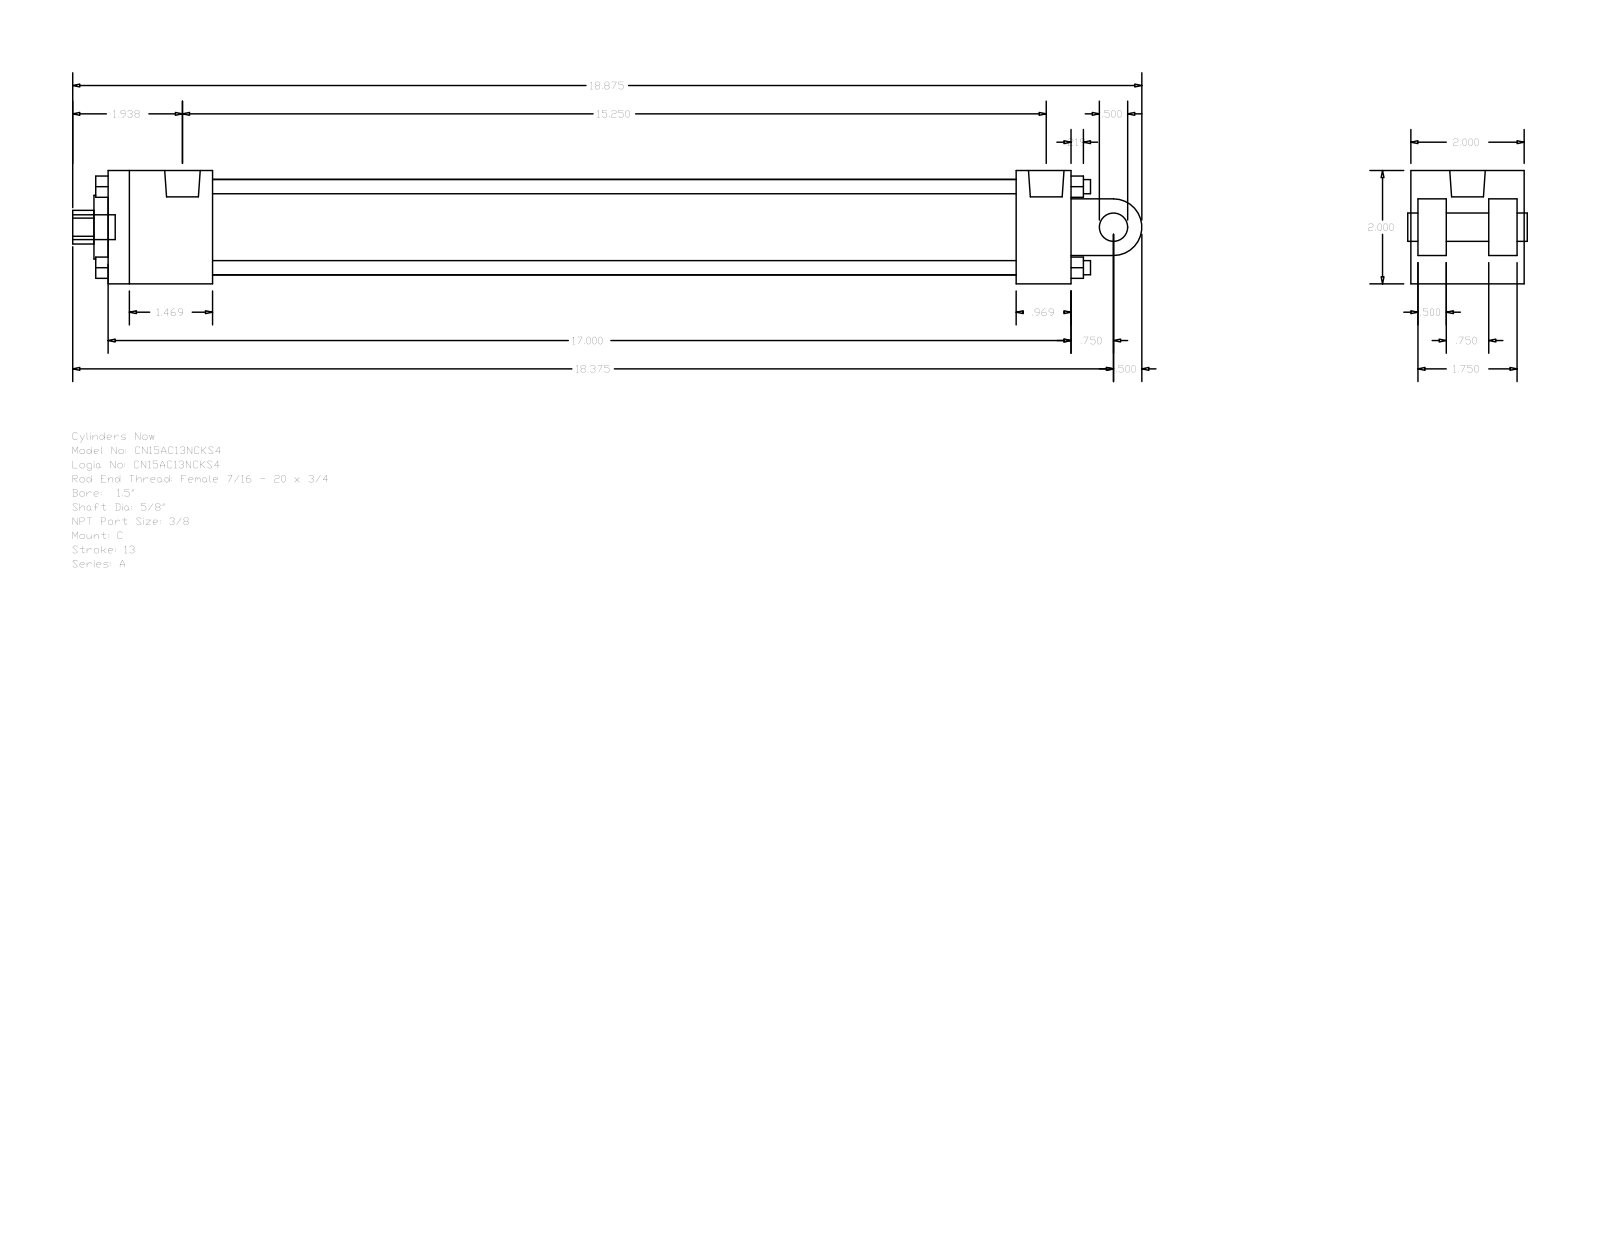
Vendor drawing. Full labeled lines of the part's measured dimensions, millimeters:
Part name (STEP PRODUCT): A_C__0150_0.625
STEP written by: GSSL Pune (CONFIG_CONTROL_DESIGN)
Units: millimetres
Bodies: 0 solids, 135 faces (102 planar, 33 cylindrical, 0 other)
Overall size (bounding box): 479.43 × 50.8 × 50.8
Round holes (diameter × count): ⌀5.56 ×2, ⌀15.88 ×1, ⌀15.93 ×1, ⌀28.57 ×1, ⌀42.93 ×1
Round bosses / shafts (diameter × count): ⌀6.35 ×4, ⌀5.56 ×2, ⌀15.93 ×1, ⌀12.7 ×1, ⌀11.11 ×1
Partial cylindrical surfaces — rounded edges, fillets, slot ends (radius × count): R7.54 ×1, R12.7 ×1
Main face-to-face distances: 50.8, 12.7, 431.8, 3.17, 15.87, 34.93, 47.63, 31.76, 407.19, 24.61
Hole centre spacings: 3.97
